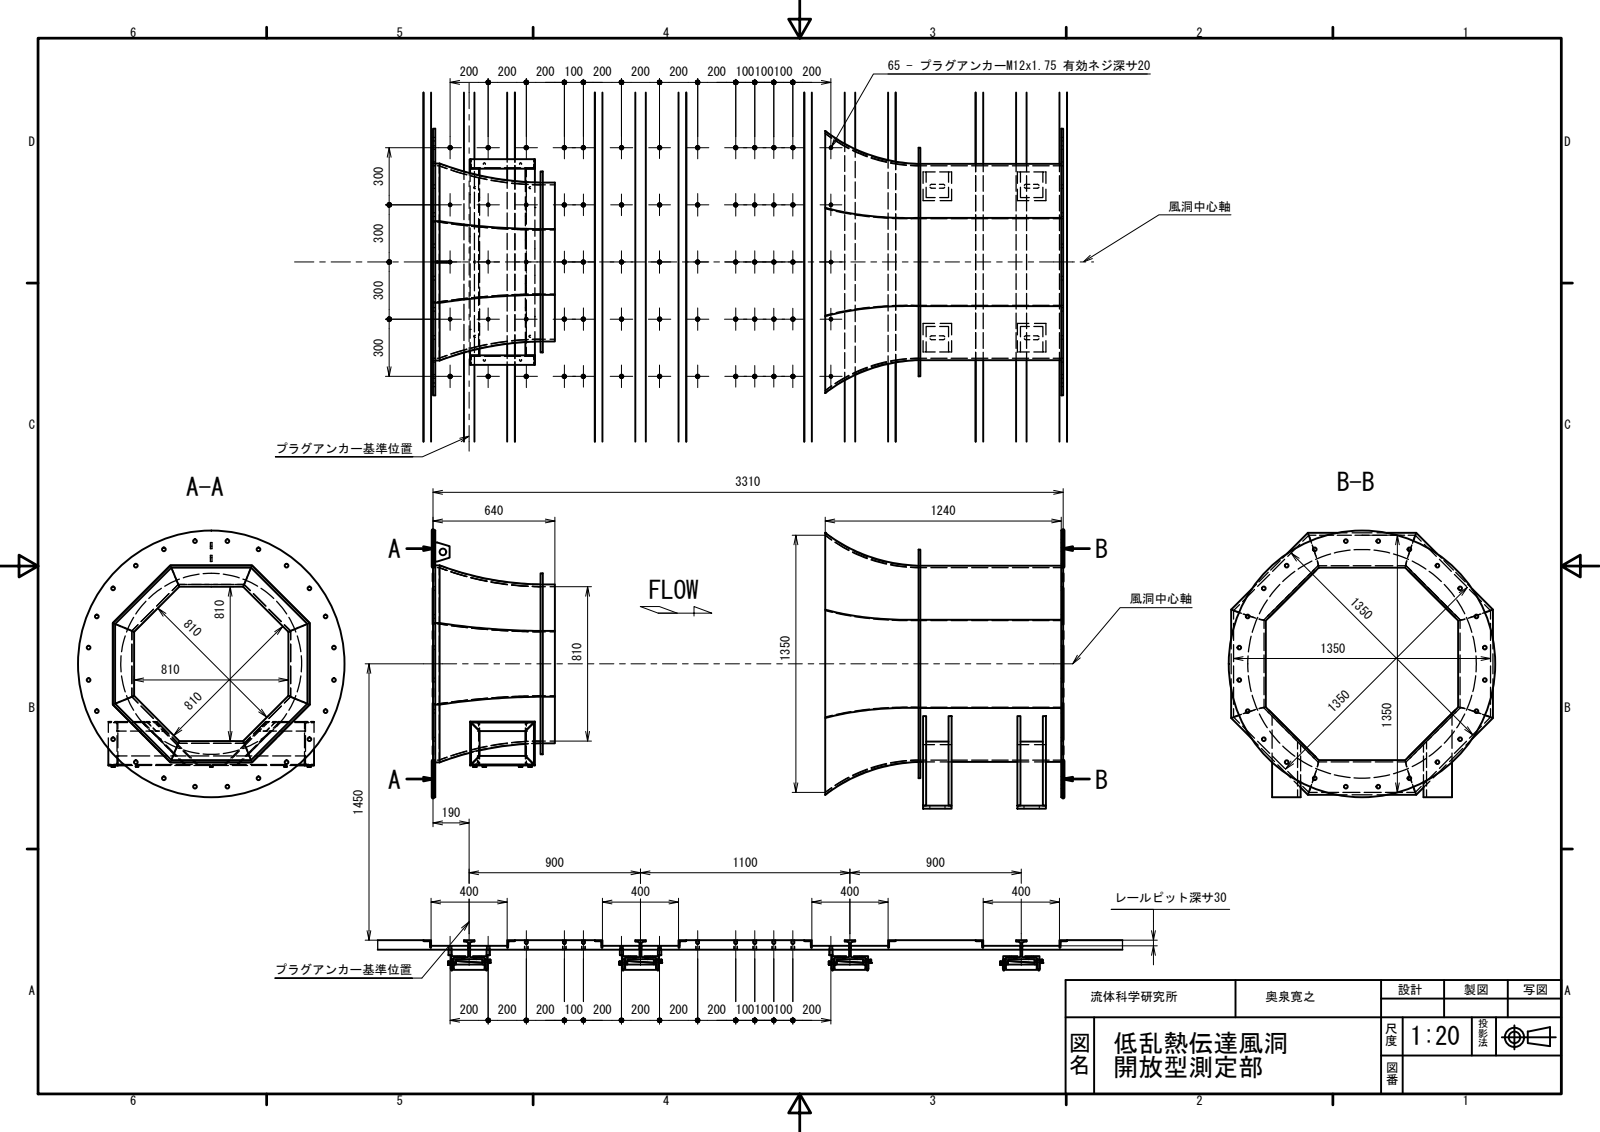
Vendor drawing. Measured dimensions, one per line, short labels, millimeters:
name: Ｒ375738-03-02; Ｒ375738-03-03; Ｒ375738-03-04; Ｒ375738-03-004 (+8 more)
written by: Autodesk Inventor 2015 (AUTOMOTIVE_DESIGN)
unit: mm
bodies: 658 solids, 7745 faces (5191 planar, 1459 cylindrical, 1095 other)
size: 6000 × 6000 × 2308.71
volume: 1 697 000 000 mm³; area: 119 900 000 mm²
holes: 201× ⌀11, 65× ⌀10.11, 65× ⌀18, 24× ⌀9, 24× ⌀19, 10× ⌀8.5, 10× ⌀10, 1× ⌀35
bosses: 65× ⌀17.3, 24× ⌀16, 24× ⌀10, 1× ⌀1400, 1× ⌀1200, 1× ⌀950
rounds: 48× R3, 16× R6, 16× R6.5, 16× R7, 16× R8.5, 8× R3.5, 8× R10
face distances: 50, 20, 30, 10, 900, 5, 2000, 25, 45, 100
hole spacings: 1125.83, 1201.04, 1255.7, 169.68, 500, 791.39, 336.46, 650
